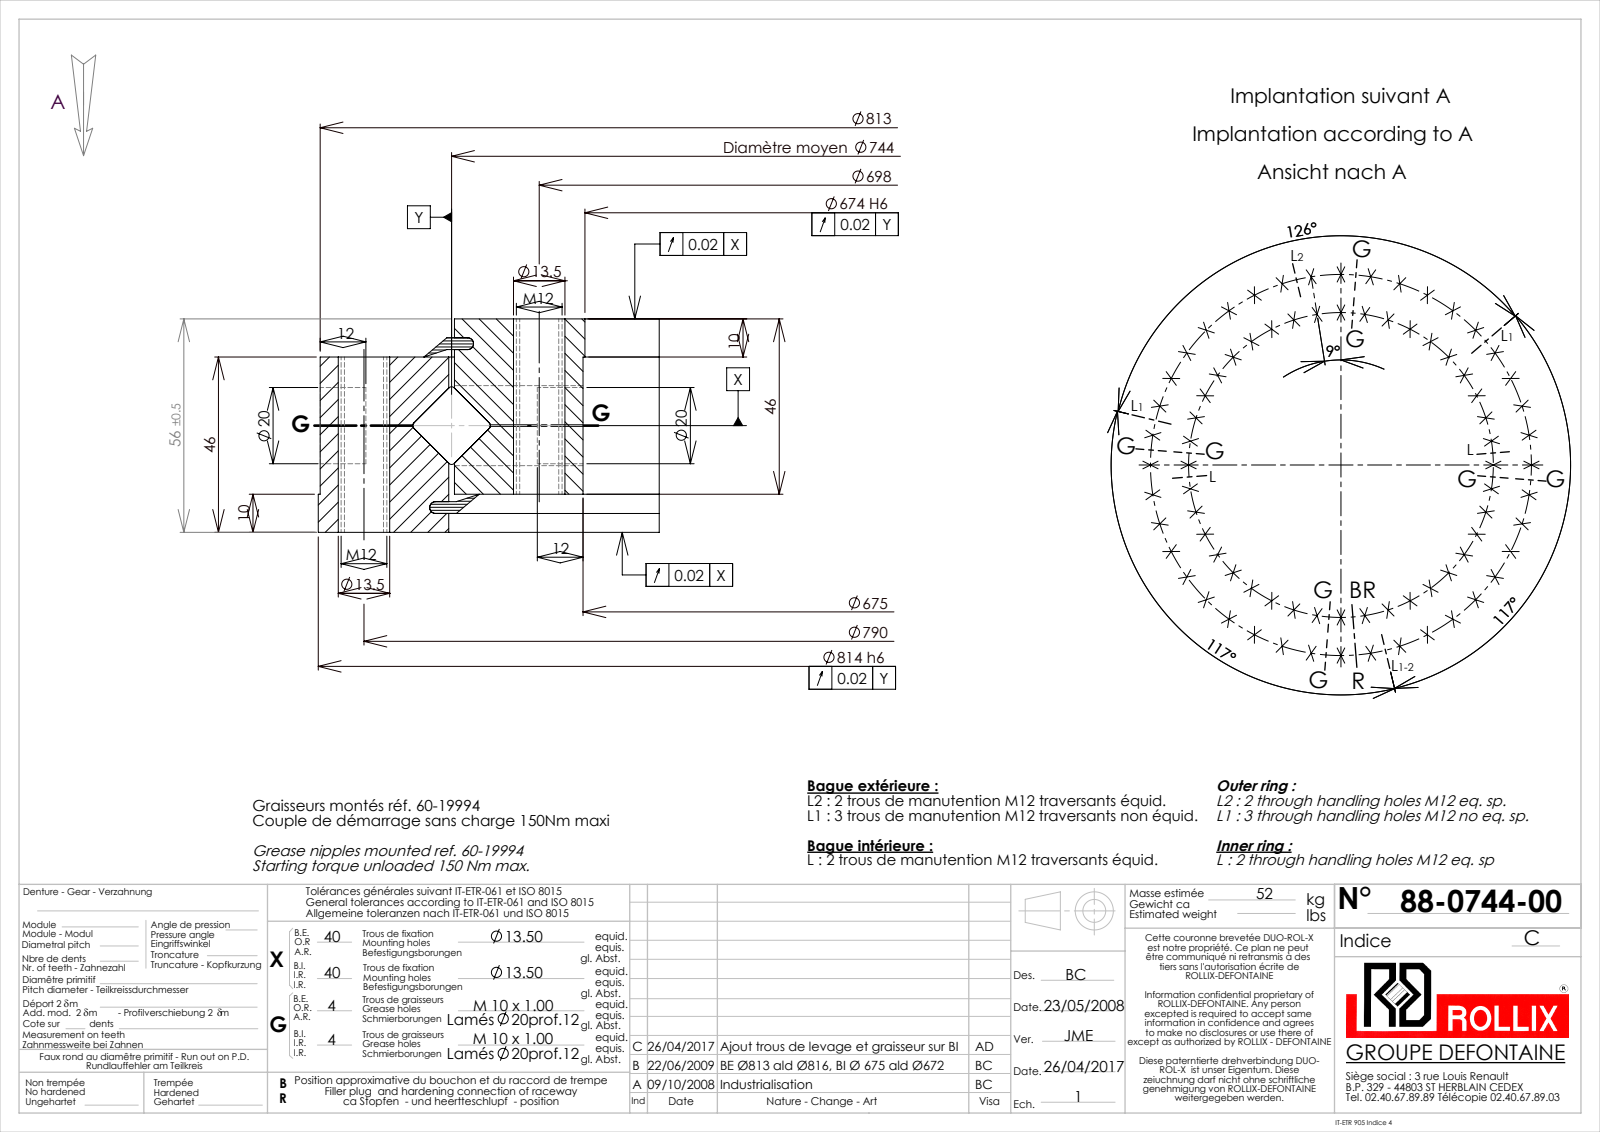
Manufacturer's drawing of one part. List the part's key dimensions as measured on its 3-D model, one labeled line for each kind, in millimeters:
Part name (STEP PRODUCT): 88-0744-00
STEP written by: SolidWorks 2016 (CONFIG_CONTROL_DESIGN)
Units: millimetres
Bodies: 13 solids, 491 faces (104 planar, 246 cylindrical, 141 other)
Overall size (bounding box): 814 × 814 × 56
Volume: 6 324 000 mm³ · Surface area: 1 122 000 mm²
Round holes (diameter × count): ⌀13.5 ×80, ⌀9 ×8, ⌀20 ×8, ⌀10.2 ×6, ⌀674 ×1, ⌀675 ×1, ⌀745.5 ×1, ⌀755.5 ×1
Round bosses / shafts (diameter × count): ⌀10 ×4, ⌀814 ×1, ⌀813 ×1, ⌀742.5 ×1, ⌀732.5 ×1, ⌀15 ×1
Main face-to-face distances: 46, 10, 36, 56, 8.05, 47.95, 1.95, 37.95, 4.95, 51.05
Hole centre spacings: 395, 302.32, 61.98, 558.62, 244.13, 513.07, 184.42, 358.66
